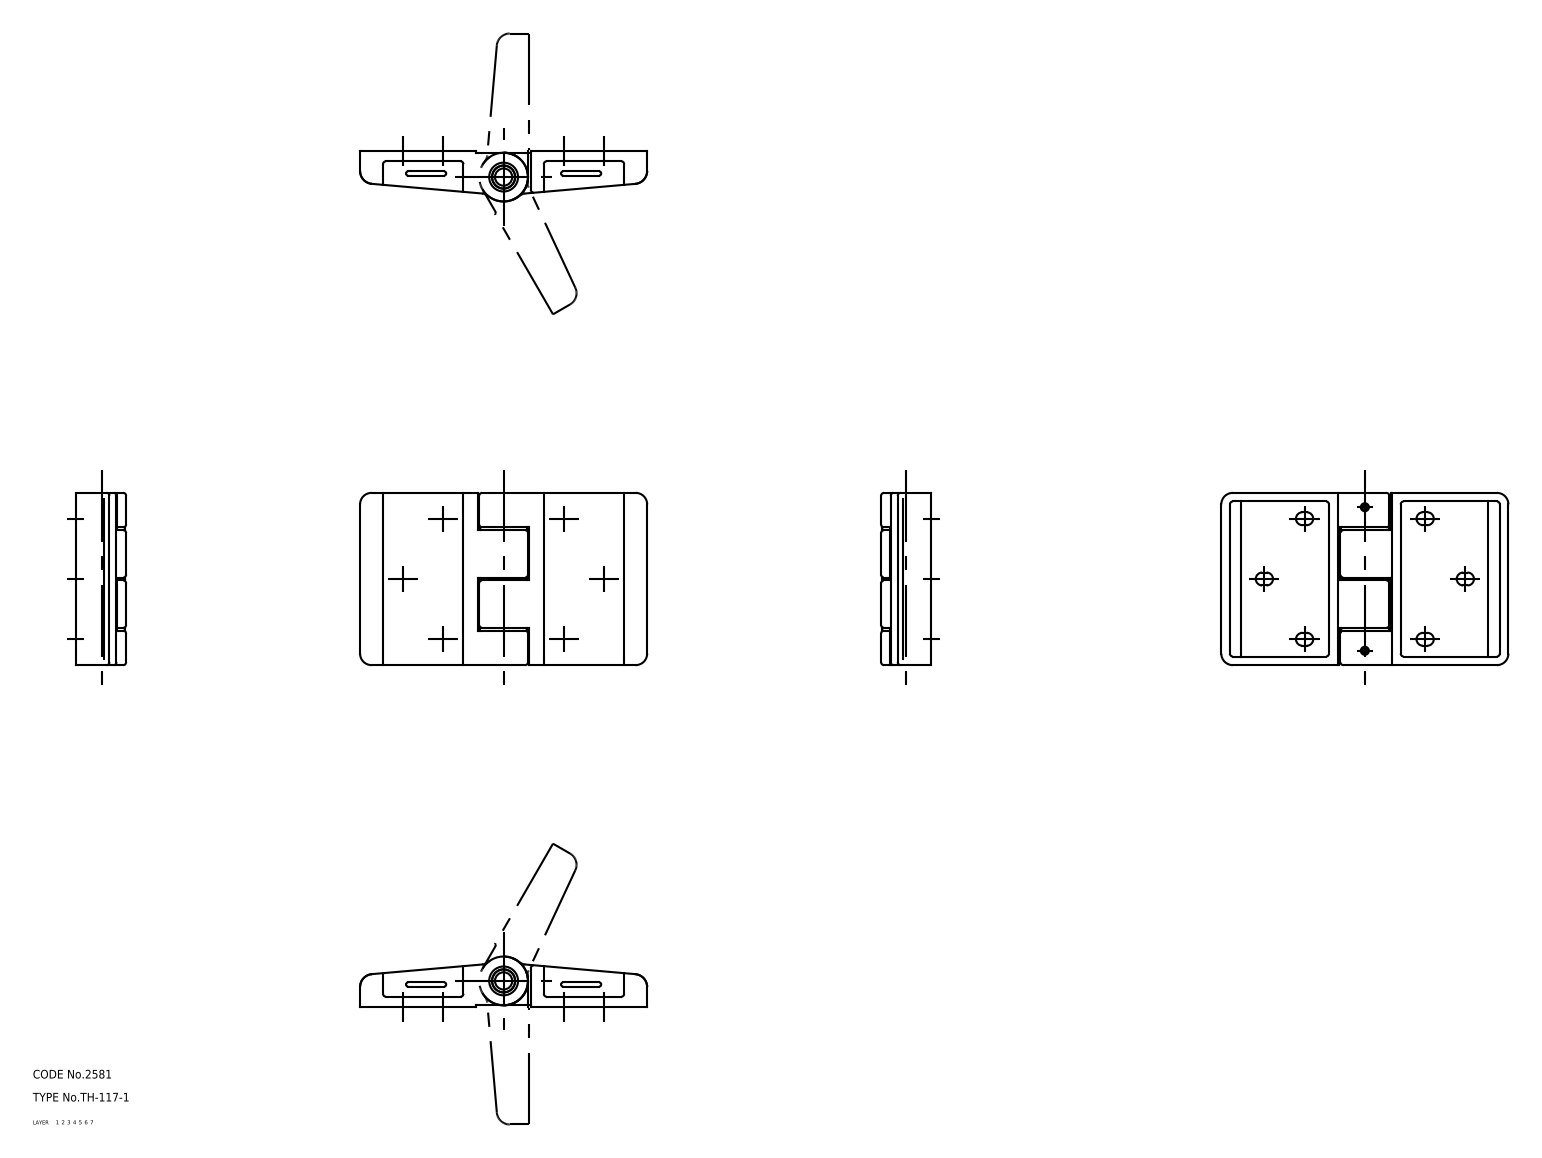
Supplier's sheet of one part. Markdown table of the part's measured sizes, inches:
| quantity | value |
| --- | --- |
| part name | washer; shaft; hinge piece_mr-1; hinge piece (+3 more) |
| STEP written by | CADfix (AUTOMOTIVE_DESIGN) |
| units | inches |
| bodies | 8 solids, 270 faces (0 planar, 0 cylindrical, 270 other) |
| overall size | 3.937 × 2.362 × 0.689 |
| volume | 4.466 in³ |
| surface area | 50.55 in² |
